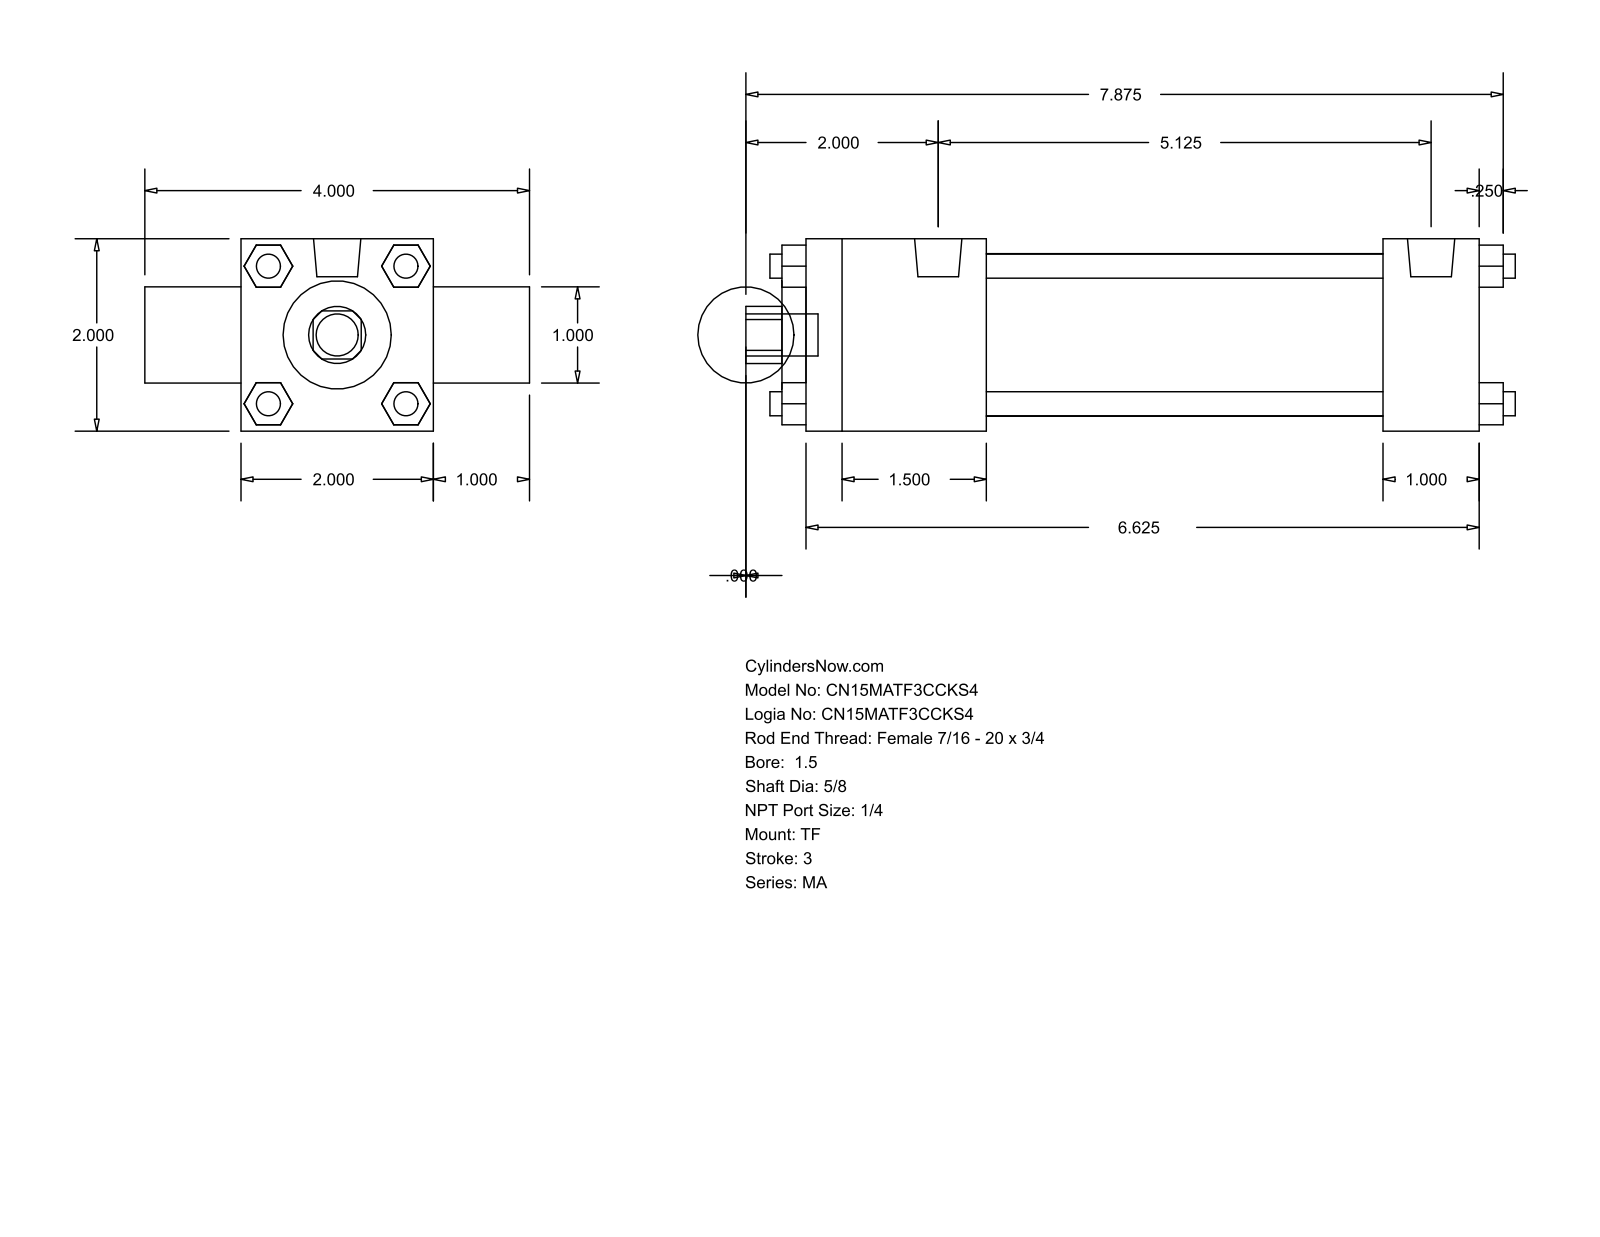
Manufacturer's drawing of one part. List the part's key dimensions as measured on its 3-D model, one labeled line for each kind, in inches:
Part name (STEP PRODUCT): MA_TF__0150_0.625
STEP written by: GSSL Pune (CONFIG_CONTROL_DESIGN)
Units: inches
Bodies: 0 solids, 120 faces (92 planar, 28 cylindrical, 0 other)
Overall size (bounding box): 8 × 4 × 2
Round holes (diameter × count): ⌀0.625 ×1, ⌀1 ×1, ⌀1.125 ×1, ⌀1.69 ×1
Round bosses / shafts (diameter × count): ⌀0.25 ×4, ⌀0.313 ×3, ⌀0.492 ×2, ⌀0.437 ×1
Partial cylindrical surfaces — rounded edges, fillets, slot ends (radius × count): R0.297 ×1
Main face-to-face distances: 2, 1, 7, 7.25, 0.25, 3, 1.875, 6, 4.125, 5.125
